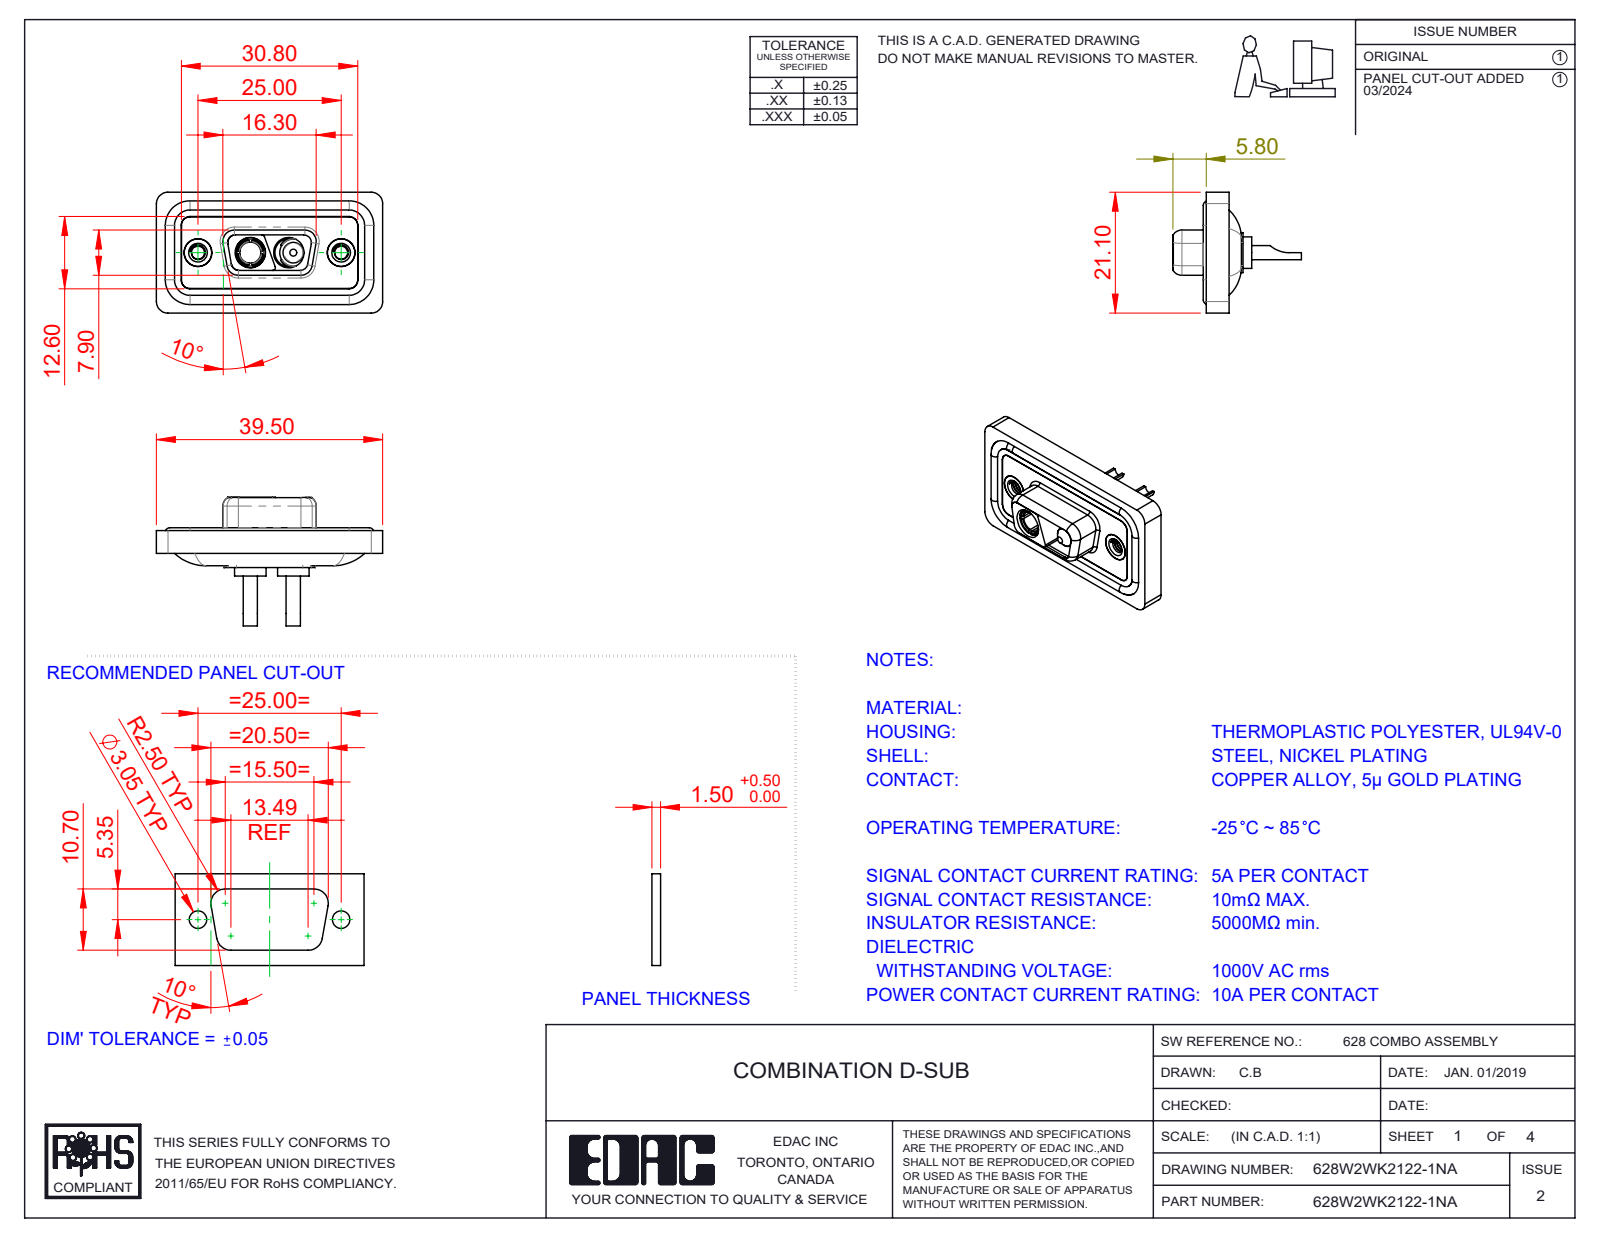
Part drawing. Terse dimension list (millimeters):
name: 628Combo Shell Rear_09 Contacts; 628Combo Waterproof Housing_09 Contacts; Power Pin_10A SC; 628W2WK2122-1NA (+4 more)
written by: SolidWorks 2023 (CONFIG_CONTROL_DESIGN)
unit: mm
bodies: 11 solids, 508 faces (148 planar, 239 cylindrical, 121 other)
size: 39.5 × 22.45 × 21.1
volume: 4 599 mm³; area: 7 437 mm²
holes: 4× ⌀4.85, 2× ⌀1.7, 2× ⌀2.26, 2× ⌀4, 2× ⌀4.05, 2× ⌀5, 2× ⌀5.3, 1× ⌀3.7
bosses: 4× ⌀1.6, 2× ⌀5.5, 2× ⌀5.2, 2× ⌀4.95, 2× ⌀4.8, 2× ⌀4.75, 2× ⌀3.75, 2× ⌀2.5
rounds: 22× R1.5, 18× R2, 8× R1.35, 8× R1.6, 6× R0.5, 4× R0.25, 4× R0.6, 4× R0.65
face distances: 0.4, 1.1, 2.9, 1.6, 0.5, 1.8, 5.65, 1.5, 5.35, 3.1
hole spacings: 9.14, 15.86, 6.72, 25
